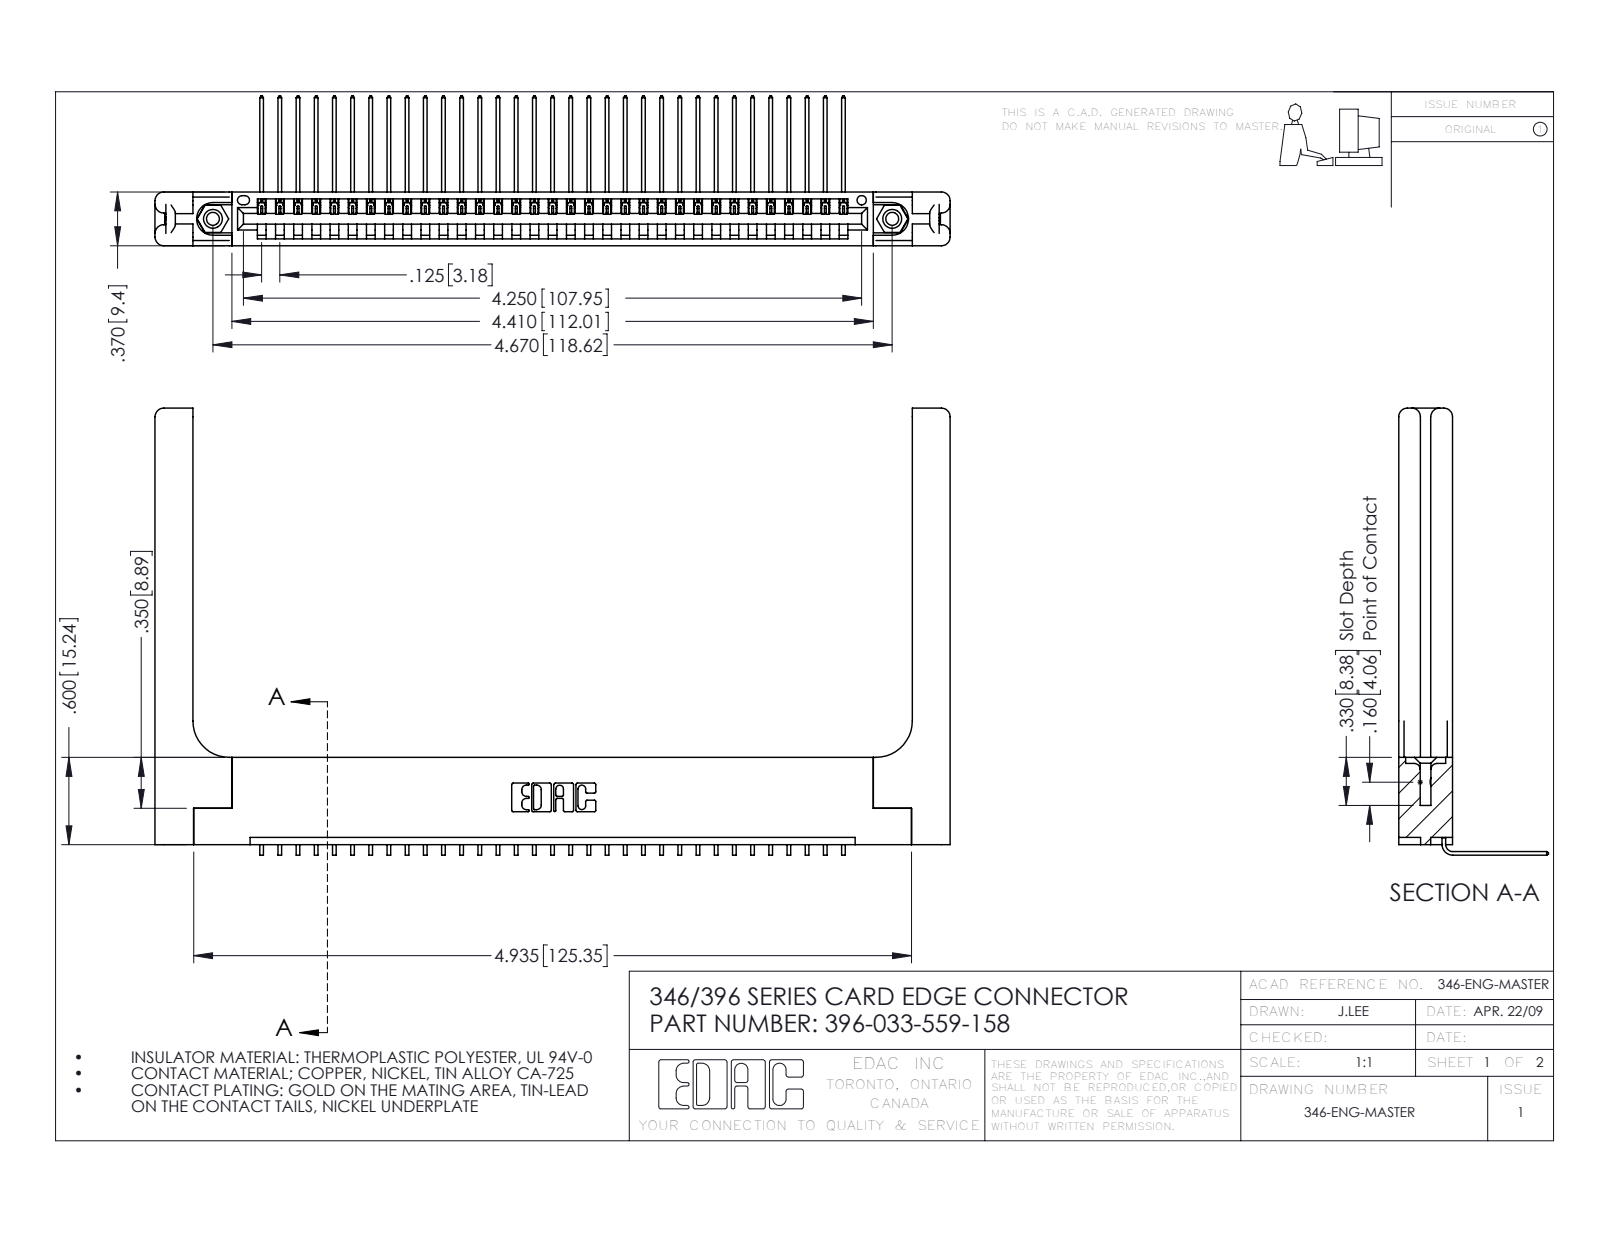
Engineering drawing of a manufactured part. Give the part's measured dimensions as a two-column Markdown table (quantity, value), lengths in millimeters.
| quantity | value |
| --- | --- |
| part name | 345-292-001_558 559 Tail - 1; 346-220-058_345-220-058; 346 Part_Flush Mounting Lugs - 0.156 Dia-TH; 345-250-001_345-250-001-102 (+1 more) |
| STEP written by | SolidWorks 2016 (CONFIG_CONTROL_DESIGN) |
| units | millimeters |
| bodies | 38 solids, 2358 faces (1610 planar, 688 cylindrical, 60 other) |
| overall size | 138.8 × 78.1 × 26.2 |
| volume | 20 860 mm³ |
| surface area | 22 400 mm² |
| round holes (diameter × count) | 2.3 × 2, 3.2 × 2, 4 × 2, 1.6 × 1 |
| round bosses / shafts (diameter × count) | 3.9 × 2 |
| partial cylindrical surfaces (radius × count) | 0.2 × 66, 0.3 × 22, 1.5 × 16, 0.2 × 6, 0.8 × 6, 0.7 × 3, 0.8 × 2, 0.8 × 2 |
| main face-to-face distances | 9.4, 1.2, 1.8, 8.2, 3.8, 3.8, 0.6, 6.4, 7.6, 5.6 |
| hole center spacings | 6.2, 113.3, 118.6 |
